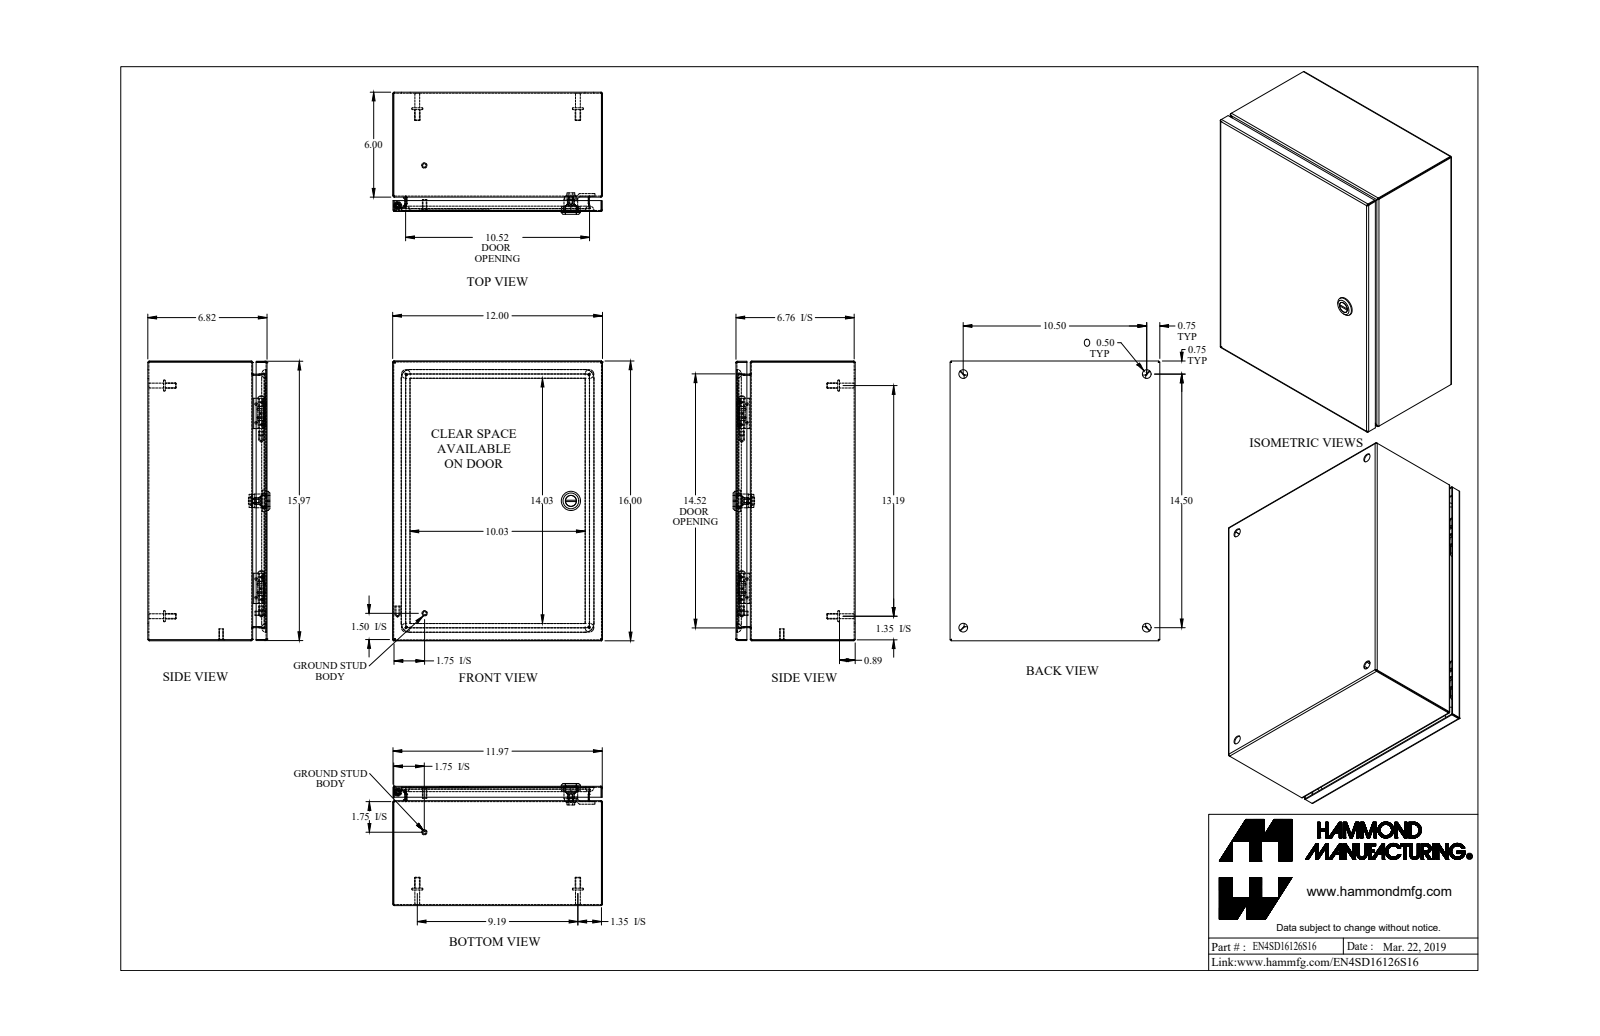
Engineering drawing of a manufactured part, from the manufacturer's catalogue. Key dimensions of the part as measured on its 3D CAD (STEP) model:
Part name (STEP PRODUCT): EN4SD16126S16_Default
STEP written by: SolidWorks 2019 (CONFIG_CONTROL_DESIGN)
Units: inches
Bodies: 22 solids, 657 faces (303 planar, 212 cylindrical, 142 other)
Overall size (bounding box): 16 × 12 × 6.981
Volume: 53.04 in³ · Surface area: 1 788 in²
Round holes (diameter × count): ⌀0.5 ×5, ⌀0.172 ×1, ⌀0.197 ×1, ⌀0.24 ×1, ⌀0.242 ×1, ⌀0.387 ×1, ⌀0.63 ×1, ⌀0.768 ×1
Round bosses / shafts (diameter × count): ⌀0.313 ×6, ⌀0.625 ×5, ⌀0.275 ×4, ⌀0.25 ×2, ⌀1.1 ×1, ⌀0.785 ×1, ⌀0.525 ×1, ⌀0.475 ×1
Partial cylindrical surfaces — rounded edges, fillets, slot ends (radius × count): R0.029 ×21, R0.086 ×21, R0.188 ×12, R0.006 ×4, R0.062 ×4, R0.25 ×4, R0.499 ×4, R0.125 ×2
Main face-to-face distances: 0.057, 0.057, 6.707, 6.764, 6.764, 6.821, 11.943, 15.943, 11.886, 12
Hole centre spacings: 7.327, 10.5, 11.904, 14.5, 17.902
